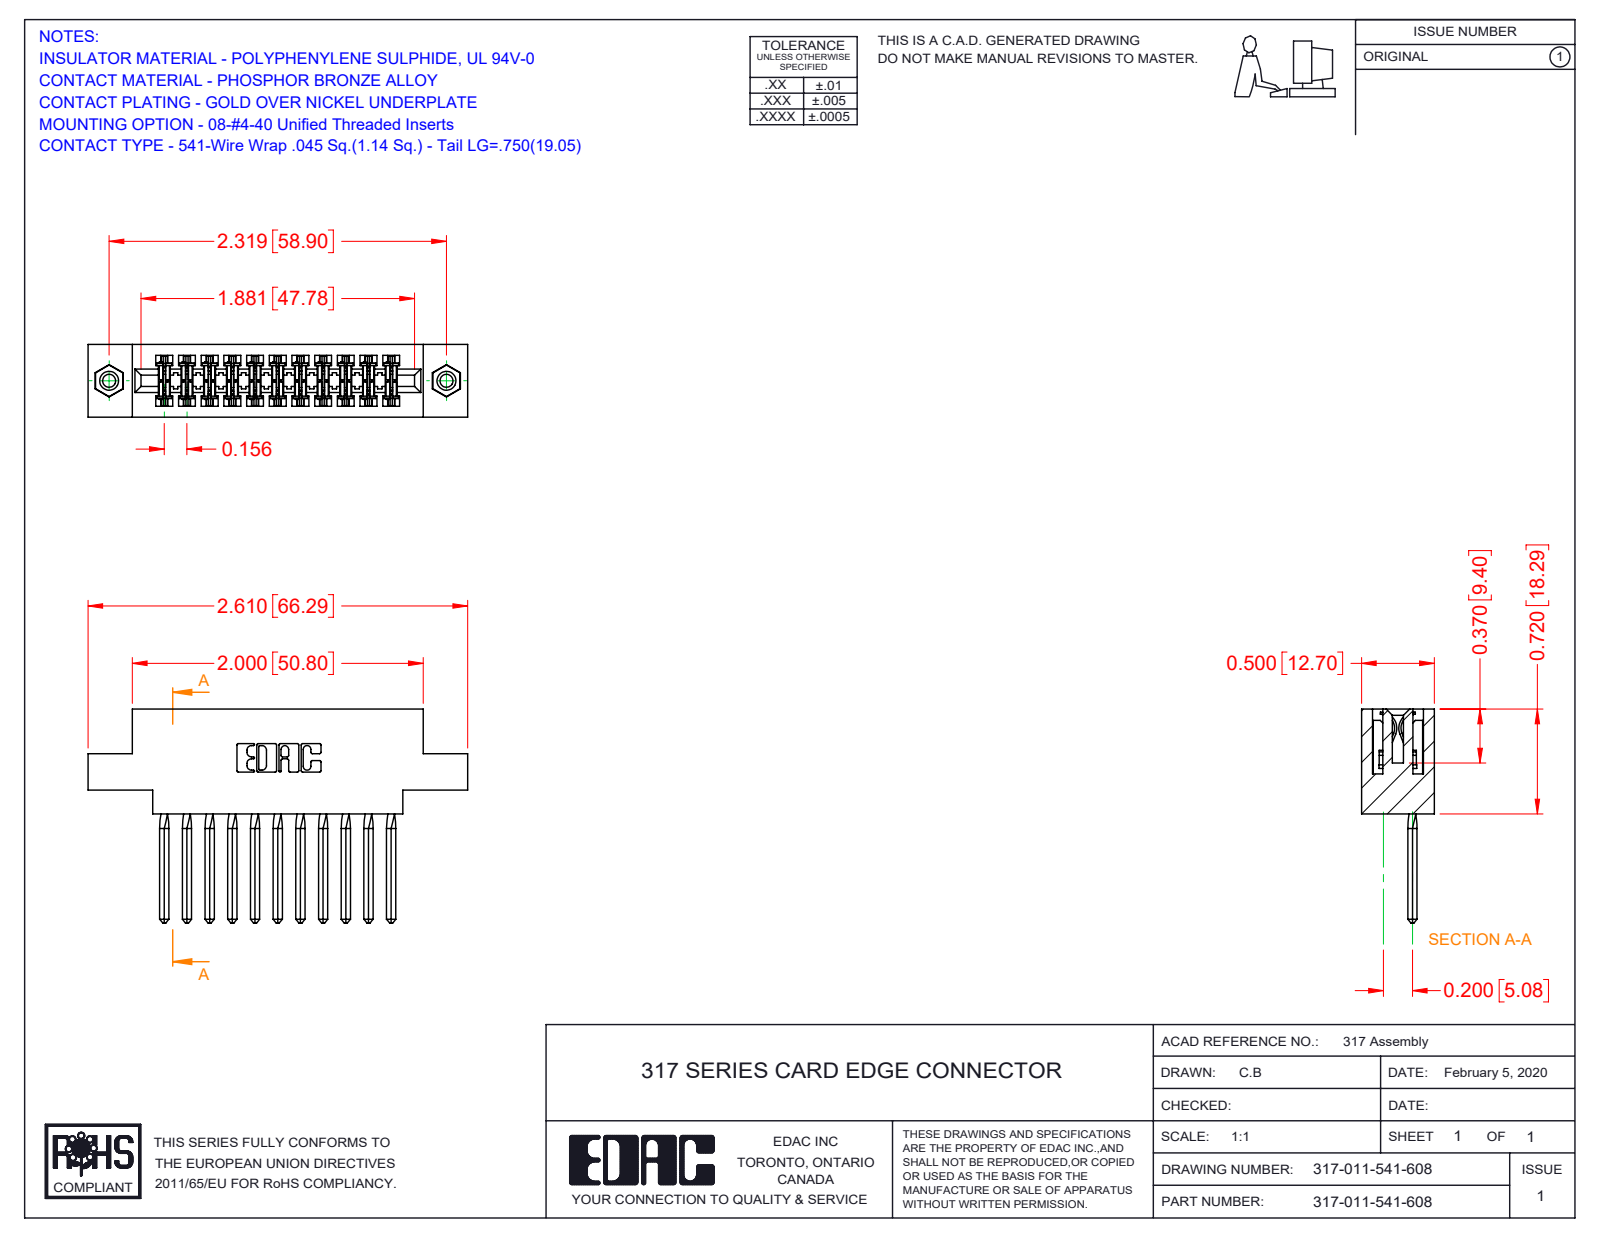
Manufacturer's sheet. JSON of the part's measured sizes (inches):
{"part_name": "317 Part_.156 Dia - TI; 317-290-002_541; 317-011-541-608; 345-250-001_345-250-003-102", "step_written_by": "SolidWorks 2016 (CONFIG_CONTROL_DESIGN)", "units": "inches", "bodies": {"solids": 14, "faces": 1834, "planar": 1454, "cylindrical": 320, "other": 60}, "overall_size": [2.61, 1.47, 0.5], "volume_in3": 0.597, "surface_area_in2": 19.88, "round_holes": [[0.089, 2], [0.125, 2], [0.156, 2]], "round_bosses_or_shafts": [[0.155, 2]], "partial_cylinders_radius": [[0.01, 22], [0.015, 22], [0.007, 6], [0.031, 6], [0.026, 3], [0.095, 2], [0.1, 2], [0.11, 2]], "face_to_face_distances": [0.5, 0.075, 0.425, 0.11, 0.22, 0.065, 0.35, 0.331, 0.156, 0.176], "hole_center_spacings": [2.319]}
